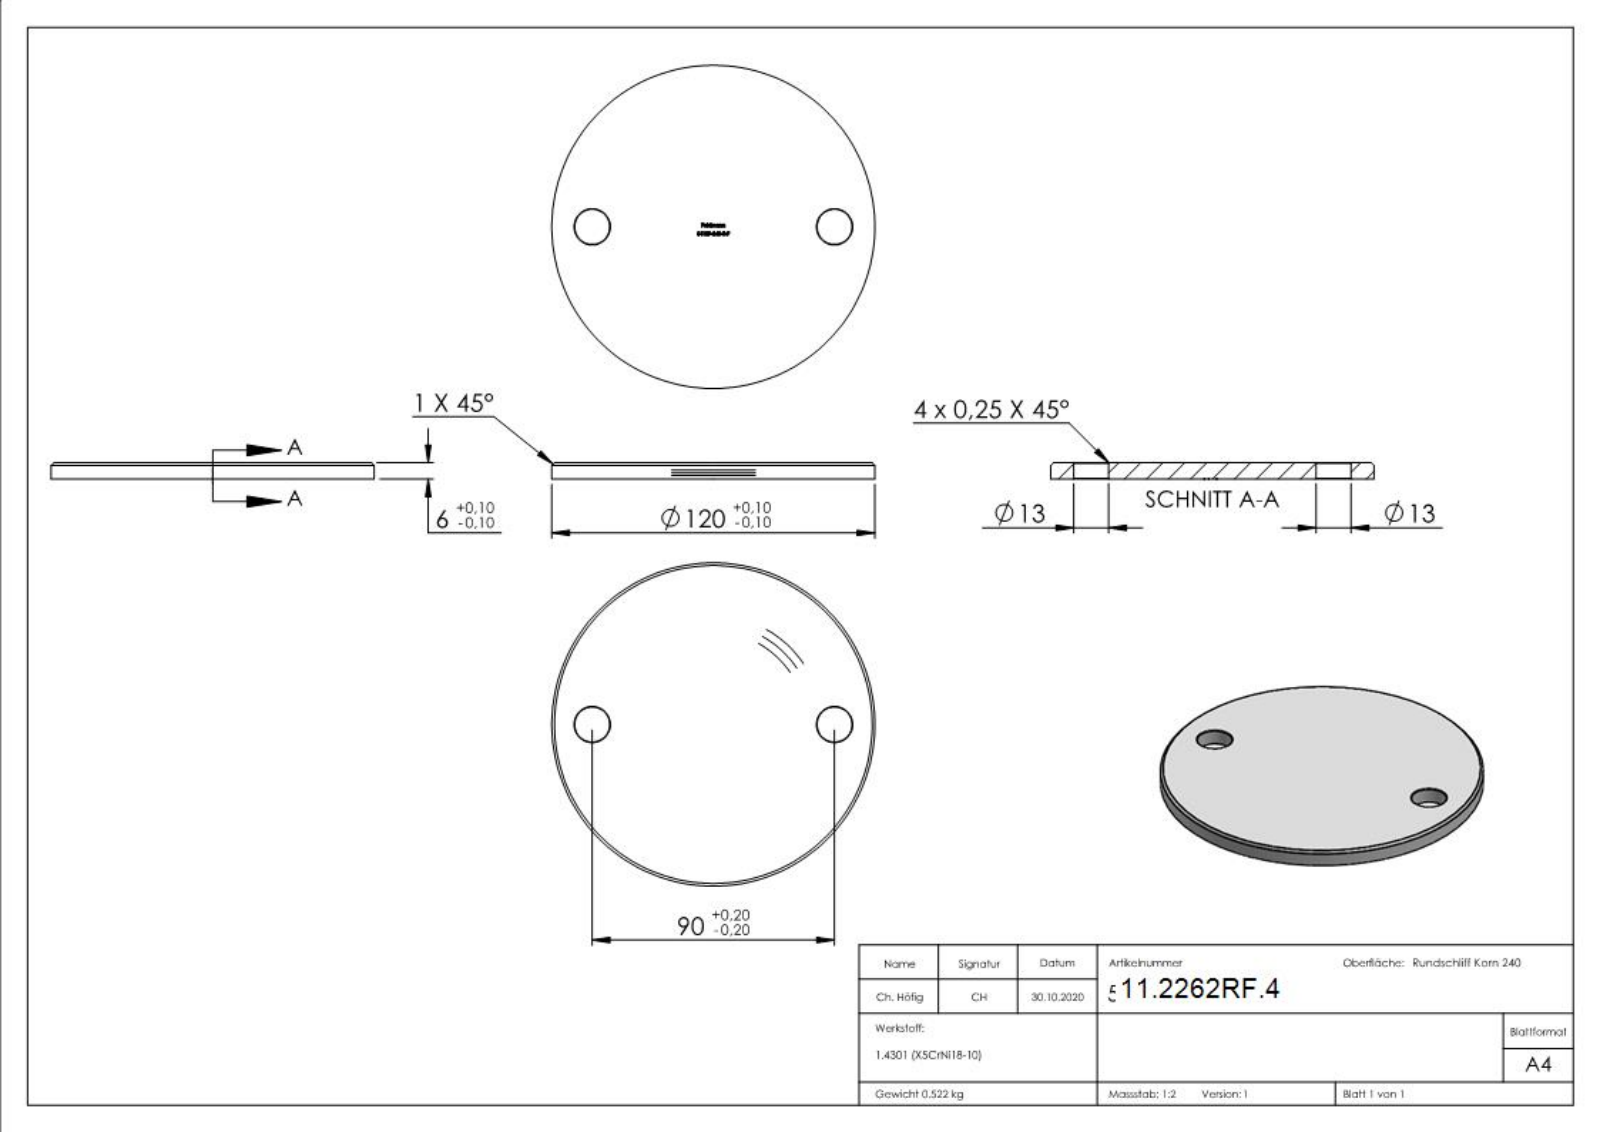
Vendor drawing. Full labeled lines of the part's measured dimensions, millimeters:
Part name (STEP PRODUCT): 54109-240-R-F
STEP written by: SolidWorks 2018 (CONFIG_CONTROL_DESIGN)
Units: millimetres
Bodies: 1 solid, 276 faces (166 planar, 6 cylindrical, 104 other)
Overall size (bounding box): 120 × 120 × 6
Volume: 66 072 mm³ · Surface area: 24 606 mm²
Round holes (diameter × count): ⌀13 ×2
Round bosses / shafts (diameter × count): ⌀120 ×1
Main face-to-face distances: 6, 5.9, 3.19, 1.19, 2.13, 5.69, 0.75, 0.58, 2.02, 1.23
Hole centre spacings: 90
